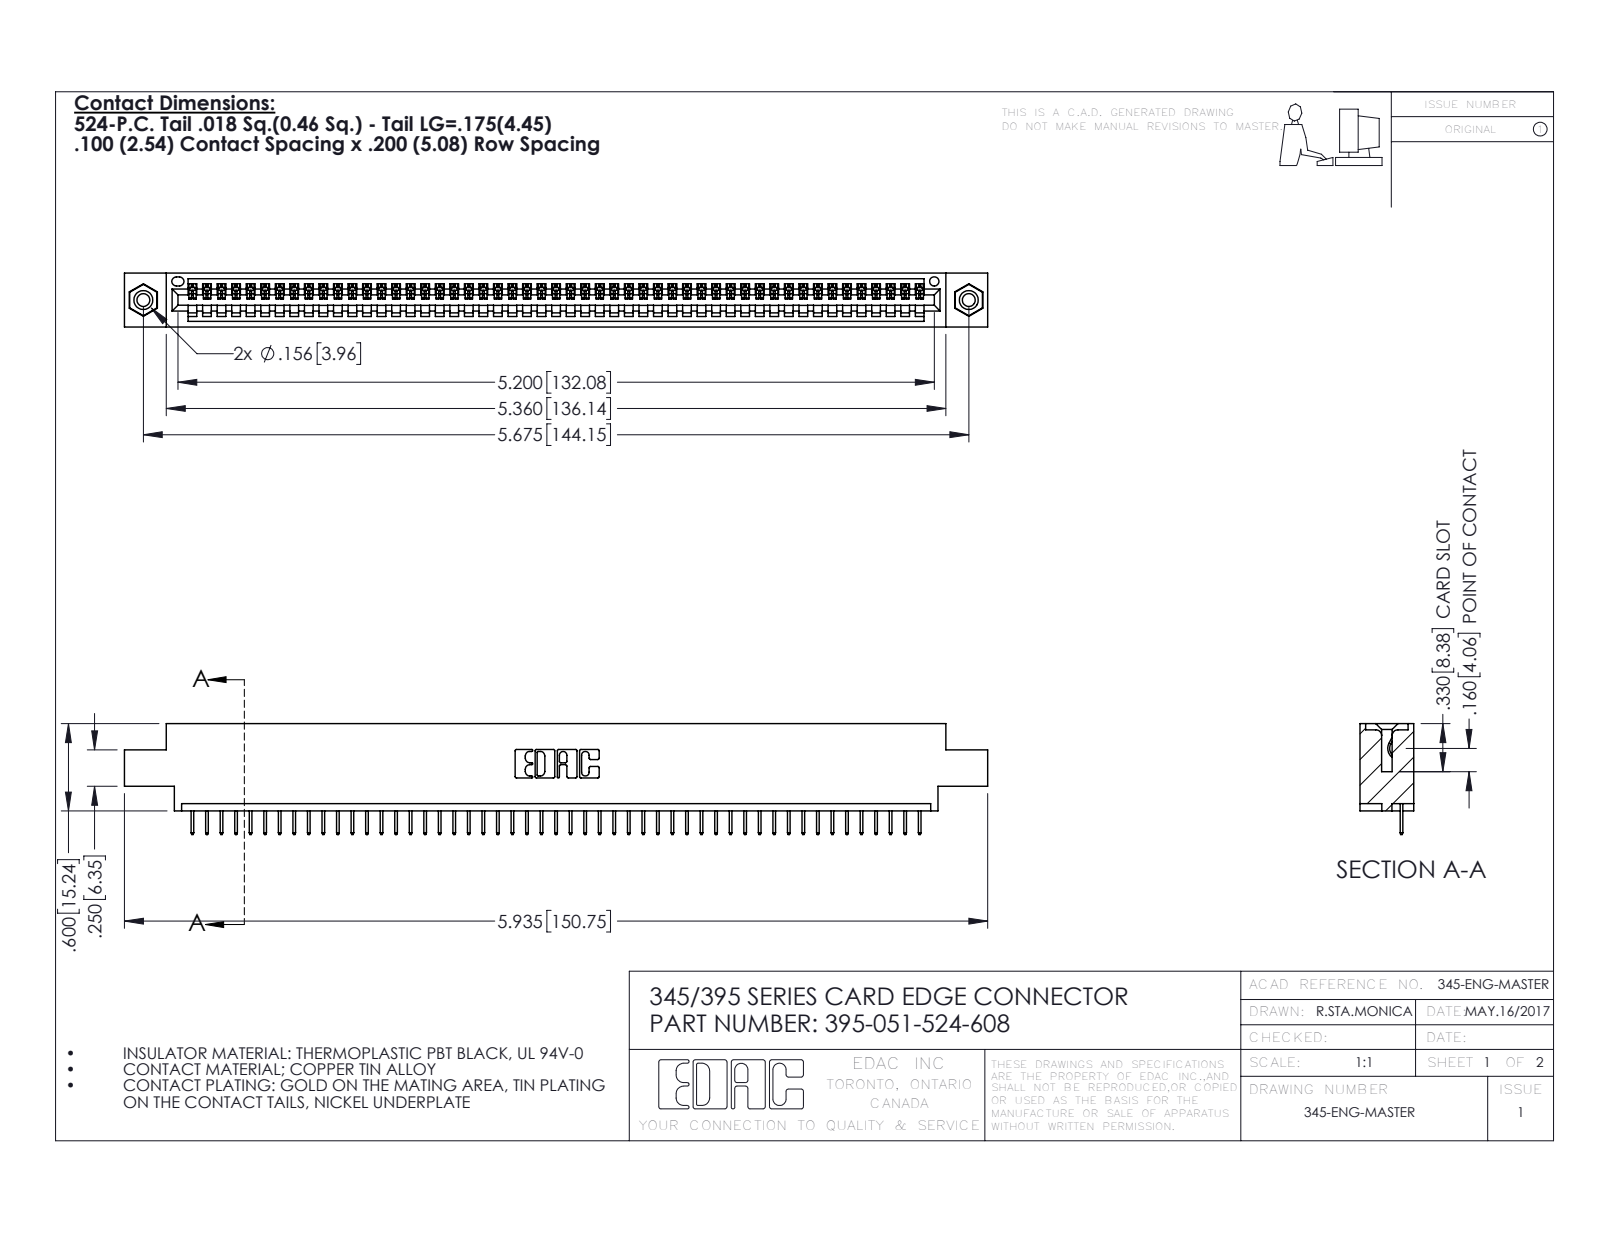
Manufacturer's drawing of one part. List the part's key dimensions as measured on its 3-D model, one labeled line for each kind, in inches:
Part name (STEP PRODUCT): 345 Part_0.170 Offset - 0.156 Dia-TI; 345-292-001_345-293-124; 345-250-001_345-250-003-102; 395-051-524-608
STEP written by: SolidWorks 2016 (CONFIG_CONTROL_DESIGN)
Units: inches
Bodies: 54 solids, 3352 faces (2462 planar, 874 cylindrical, 16 other)
Overall size (bounding box): 5.935 × 0.762 × 0.37
Volume: 0.859 in³ · Surface area: 28.4 in²
Round holes (diameter × count): ⌀0.089 ×2, ⌀0.125 ×2, ⌀0.156 ×2, ⌀0.064 ×1
Round bosses / shafts (diameter × count): ⌀0.155 ×2
Partial cylindrical surfaces — rounded edges, fillets, slot ends (radius × count): R0.006 ×102, R0.01 ×22, R0.007 ×6, R0.031 ×6, R0.026 ×3, R0.031 ×2, R0.04 ×2, R0.014 ×1
Main face-to-face distances: 0.072, 0.298, 0.37, 0.2, 0.098, 0.272, 0.025, 0.225, 0.072, 0.175
Hole centre spacings: 0.27, 5.439, 5.675
